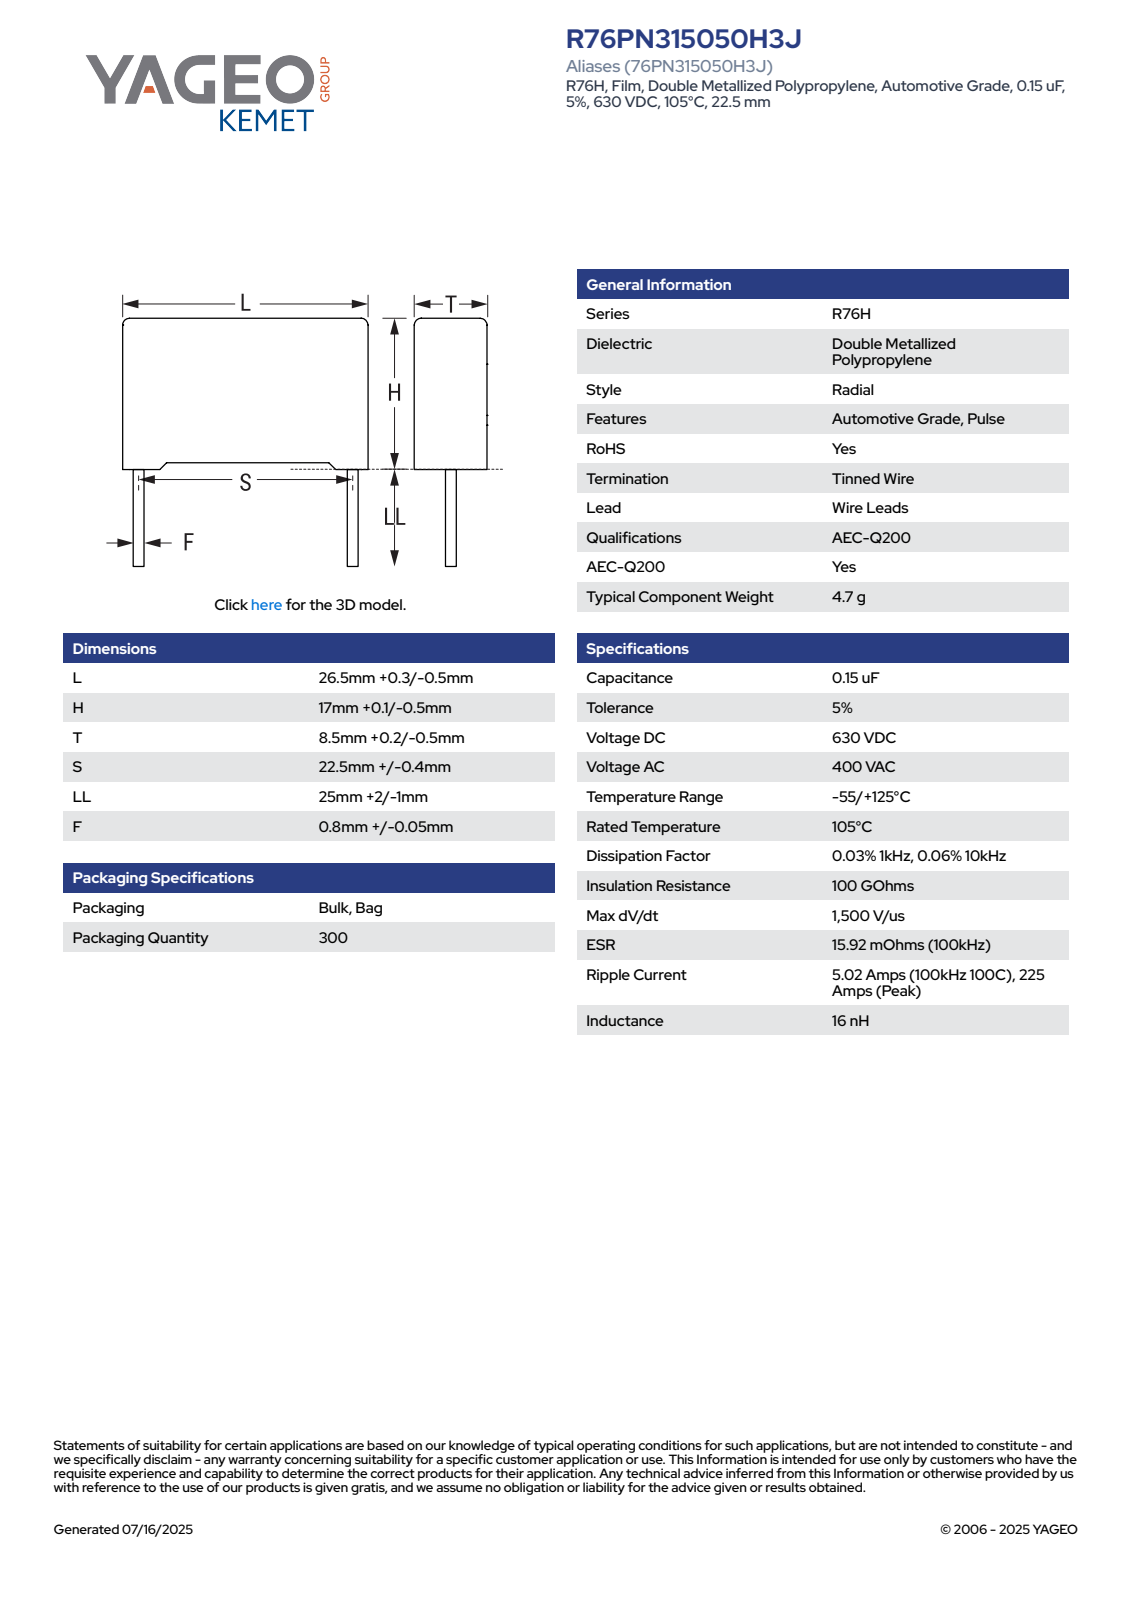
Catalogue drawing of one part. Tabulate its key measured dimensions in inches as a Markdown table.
| quantity | value |
| --- | --- |
| part name | CFR_RB2R76_26.5X17X8.5_L26.8H17.1T8.7S22.5LL27F0.85 |
| STEP written by | SolidWorks 2014 (AUTOMOTIVE_DESIGN) |
| units | inches |
| bodies | 4 solids, 85 faces (77 planar, 8 cylindrical, 0 other) |
| overall size | 1.736 × 1.055 × 0.343 |
| volume | 0.236 in³ |
| surface area | 2.902 in² |
| round bosses / shafts (diameter × count) | 0.033 × 2 |
| partial cylindrical surfaces (radius × count) | 0.02 × 4 |
| main face-to-face distances | 0.343, 0.644, 1.055, 0.65, 0.035, 0.03, 0.023, 0.673, 0.307, 0.343 |
